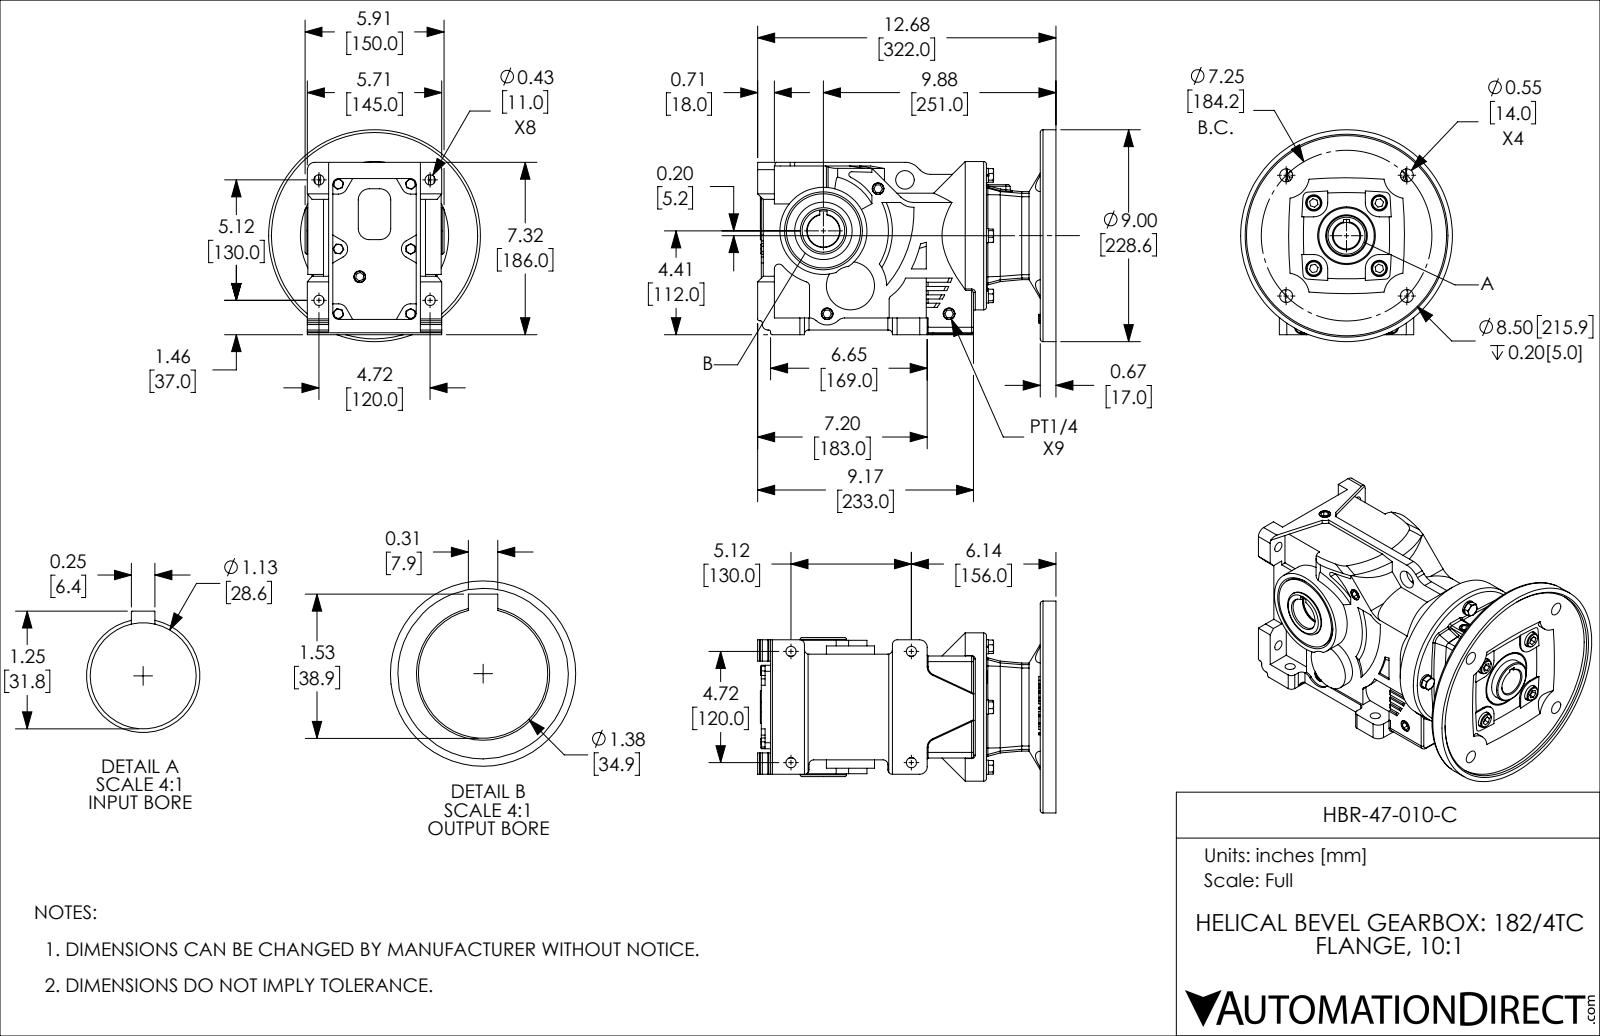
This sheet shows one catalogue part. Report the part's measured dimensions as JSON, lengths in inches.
{"part_name": "HBR-47-010-C", "step_written_by": "SolidWorks 2018 (AUTOMOTIVE_DESIGN)", "units": "inches", "bodies": {"solids": 1, "faces": 1036, "planar": 498, "cylindrical": 268, "other": 270}, "overall_size": [12.677, 9, 9], "volume_in3": 348.7, "surface_area_in2": 572.8, "round_holes": [[0.433, 8], [0.323, 4], [0.354, 4], [0.551, 4], [0.689, 4], [0.787, 1], [1.126, 1], [1.375, 1], [1.417, 1], [1.457, 1], [8.5, 1]], "round_bosses_or_shafts": [[0.63, 4], [0.606, 4], [0.315, 4], [9, 1], [6.299, 1], [3.701, 1], [3.15, 1], [2.362, 1]], "partial_cylinders_radius": [[0.079, 15], [0.197, 10], [0.394, 10], [0.472, 9], [0.157, 6], [0.039, 5], [0.689, 5], [0.256, 4]], "face_to_face_distances": [0.469, 0.197, 4.331, 0.669, 0.079, 0.118, 0.157, 0.394, 12.32, 11.85], "hole_center_spacings": [1.817, 2.563, 4.125, 4.189, 5.728, 5.118, 1.656, 1.969]}
